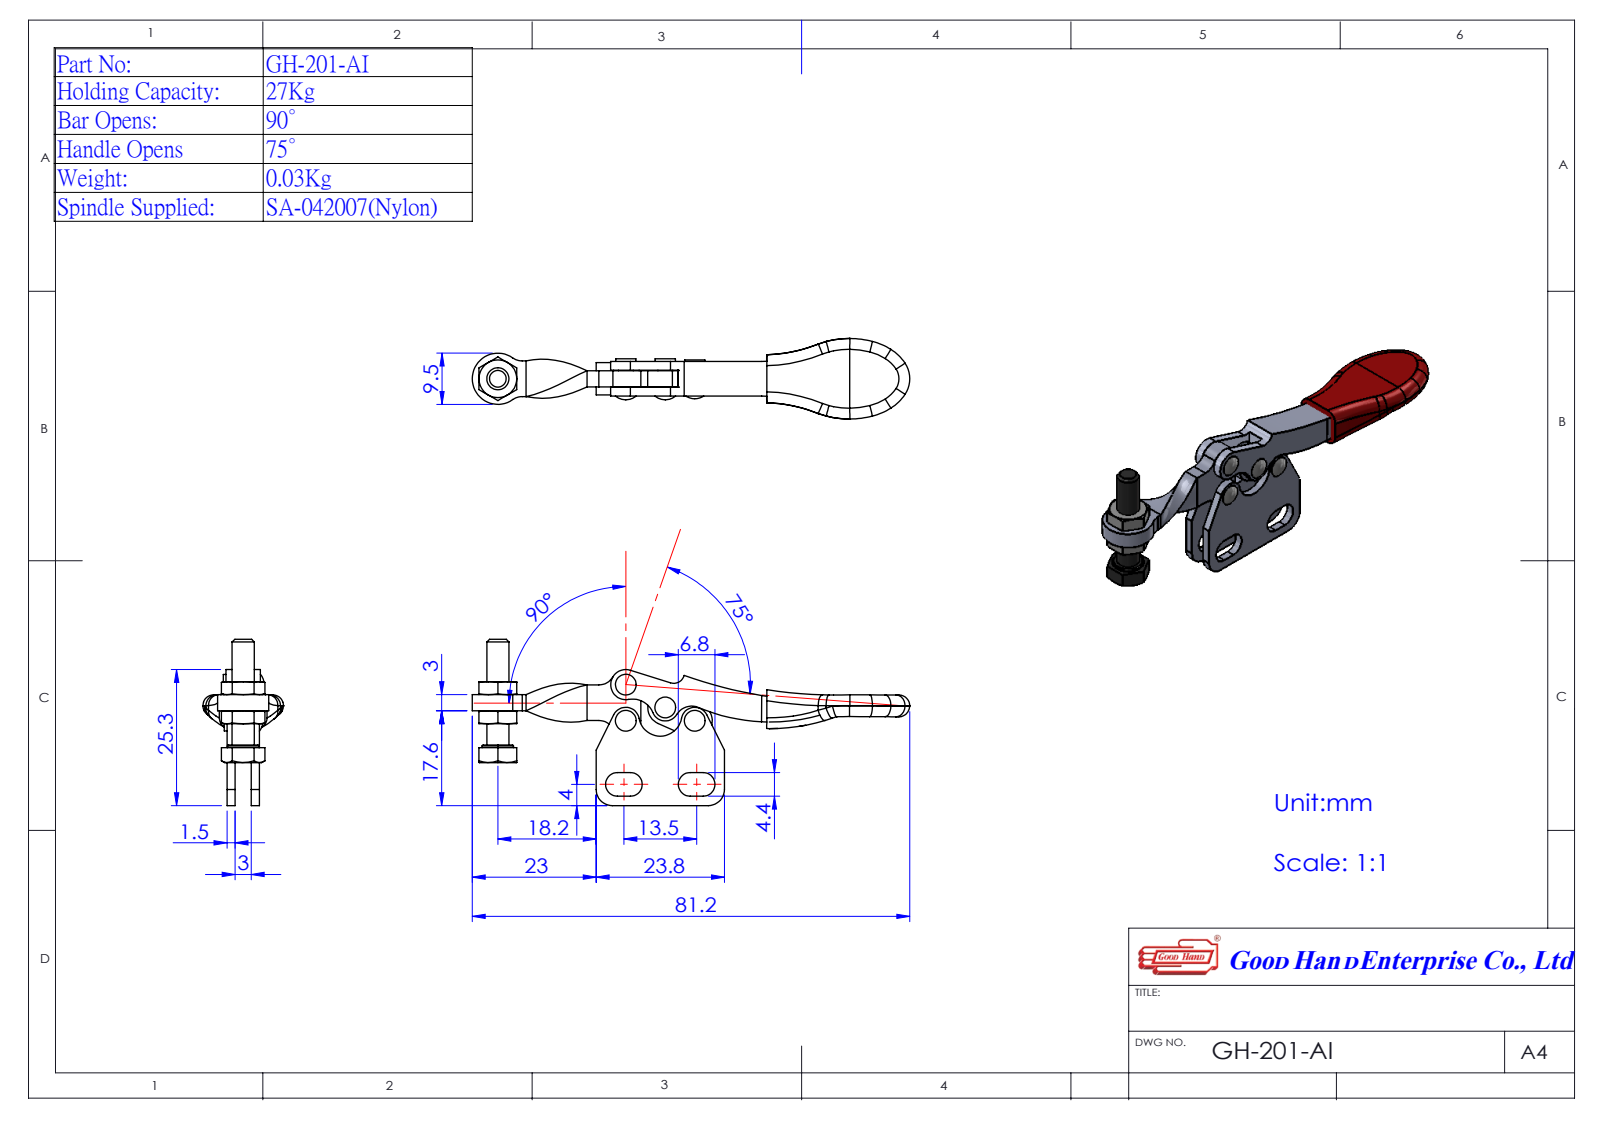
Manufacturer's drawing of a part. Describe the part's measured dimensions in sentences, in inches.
The part is named "1201A08-1^GH-201-AI(簡化); 1201A05-1^GH-201-AI(簡化); Group1^GH-201-AI(簡化); GH-201-AI(簡化) (+2 more)". Its 3-D file was written by "SolidWorks 2016 (AUTOMOTIVE_DESIGN)". It is 7 solids with 255 faces: 89 planar, 116 cylindrical and 50 other. Overall it measures 3.197 by 1.174 by 0.588 inches. Its volume is 0.142 cubic inches and its surface area 8.265 square inches. Round holes: 4 of diameter 0.098, 1 of diameter 0.169. Round bosses or shafts: 4 of diameter 0.148, 1 of diameter 0.228, 1 of diameter 0.161. Partial cylindrical surfaces (rounded edges, fillets, slot ends): 4 of radius 0.087, 4 of radius 0.118, 4 of radius 0.481, 2 of radius 0.039, 2 of radius 0.098, 2 of radius 0.11, 2 of radius 0.128, 2 of radius 0.157. The main face-to-face distances are 0.193, 0.059, 0.252, 0.126, 0.134, 0.067, 0.185, 0.118, 0.189, 0.13. The hole center spacings are 0.236, 0.264, 0.304, 0.333, 0.504, 0.569.
